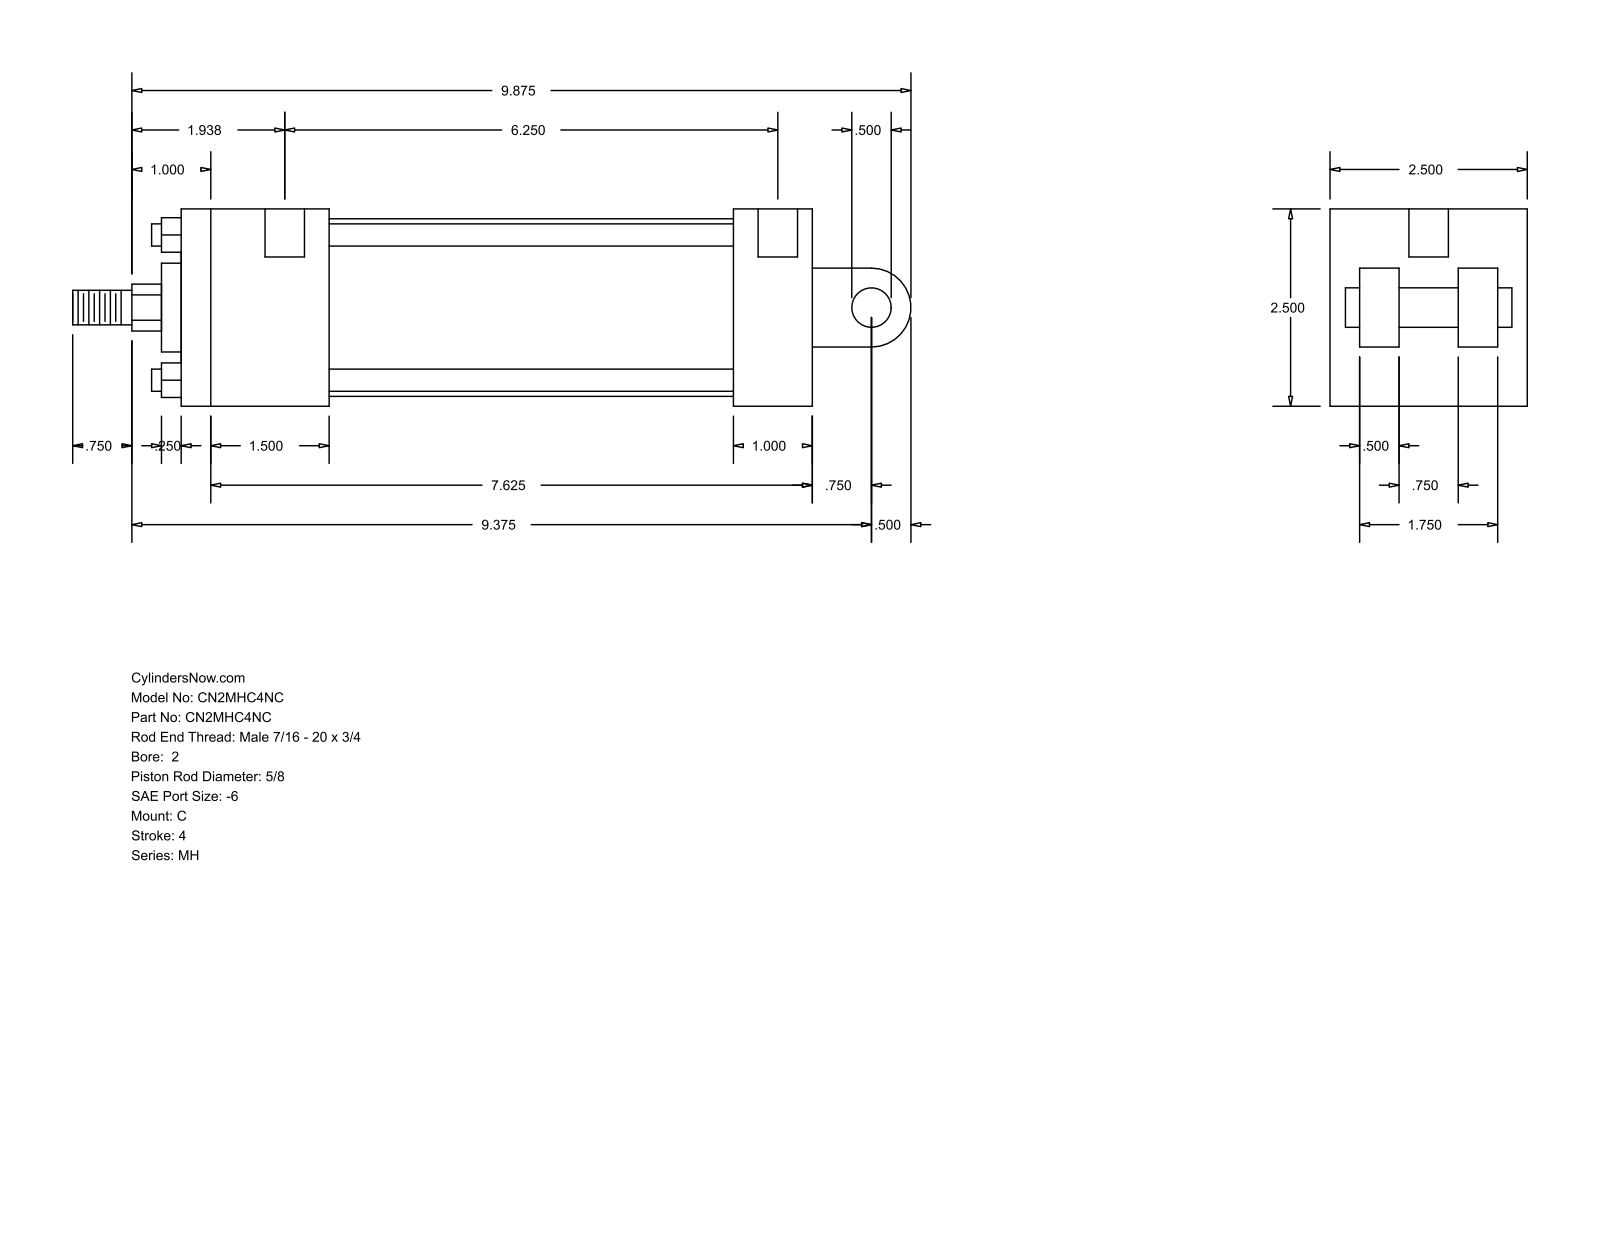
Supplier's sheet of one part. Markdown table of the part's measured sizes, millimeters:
| quantity | value |
| --- | --- |
| part name | MH_C__0200_0.625 |
| STEP written by | GSSL Pune (CONFIG_CONTROL_DESIGN) |
| units | millimeters |
| bodies | 0 solids, 99 faces (70 planar, 29 cylindrical, 0 other) |
| overall size | 269.88 × 63.5 × 63.5 |
| round holes (diameter × count) | 5.56 × 4, 12.7 × 2 |
| round bosses / shafts (diameter × count) | 7.14 × 4, 57.15 × 1, 28.57 × 1, 15.88 × 1, 12.7 × 1, 11.11 × 1 |
| partial cylindrical surfaces (radius × count) | 7.54 × 1, 12.7 × 1 |
| main face-to-face distances | 63.5, 203.19, 12.7, 47.62, 177.8, 130.18, 155.57, 25.39, 19.05, 22.22 |
| hole center spacings | 166.69, 3.18, 4.76, 158.75, 161.93, 163.51 |
